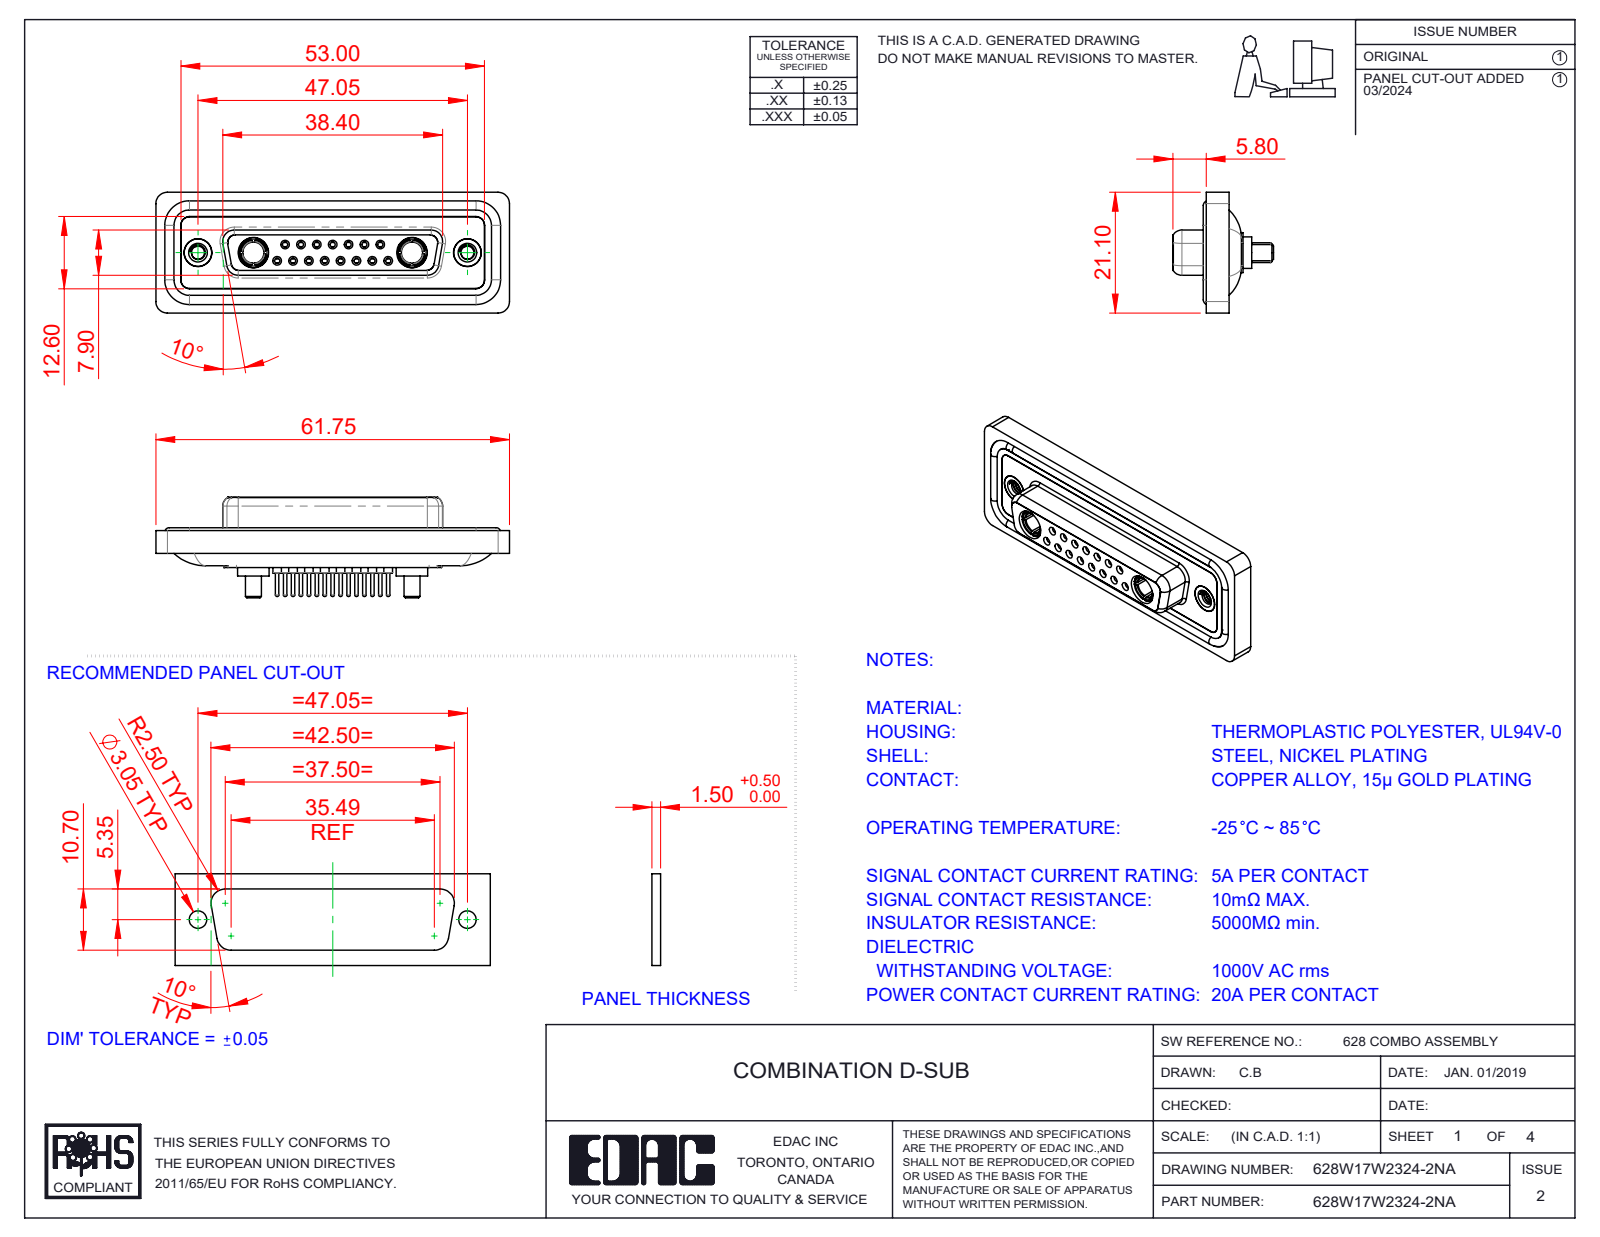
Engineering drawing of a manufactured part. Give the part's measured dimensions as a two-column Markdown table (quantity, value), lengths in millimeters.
| quantity | value |
| --- | --- |
| part name | 628Combo Shell Rear_25 Contacts; 628Combo Threaded Rivet_A; 628Combo Contact Row 1_24; 628Combo Contact Row 2_24 (+5 more) |
| STEP written by | SolidWorks 2023 (CONFIG_CONTROL_DESIGN) |
| units | millimeters |
| bodies | 26 solids, 1357 faces (388 planar, 521 cylindrical, 448 other) |
| overall size | 61.75 × 21.1 × 17.55 |
| volume | 8 326 mm³ |
| surface area | 13 853 mm² |
| round holes (diameter × count) | 0.9 × 15, 1.1 × 15, 1.5 × 15, 2 × 15, 1.6 × 8, 1.7 × 7, 4.85 × 4, 2.26 × 2, 3.7 × 2, 4 × 2, 4.05 × 2, 5 × 2 |
| round bosses / shafts (diameter × count) | 2.2 × 15, 0.6 × 15, 1.6 × 11, 5.5 × 2, 5.2 × 2, 4.96 × 2, 4.95 × 2, 4.8 × 2 |
| partial cylindrical surfaces (radius × count) | 1.5 × 22, 2 × 18, 1.35 × 8, 1.6 × 8, 0.25 × 4, 0.5 × 4, 0.6 × 4, 0.65 × 4 |
| main face-to-face distances | 0.4, 1.8, 7.45, 5.65, 6.6, 0.5, 7.05, 1.6, 2.9, 1.1 |
| hole center spacings | 3.16, 2.77, 8.31, 5.54, 5.03, 5.04, 7.49, 11.08 |
